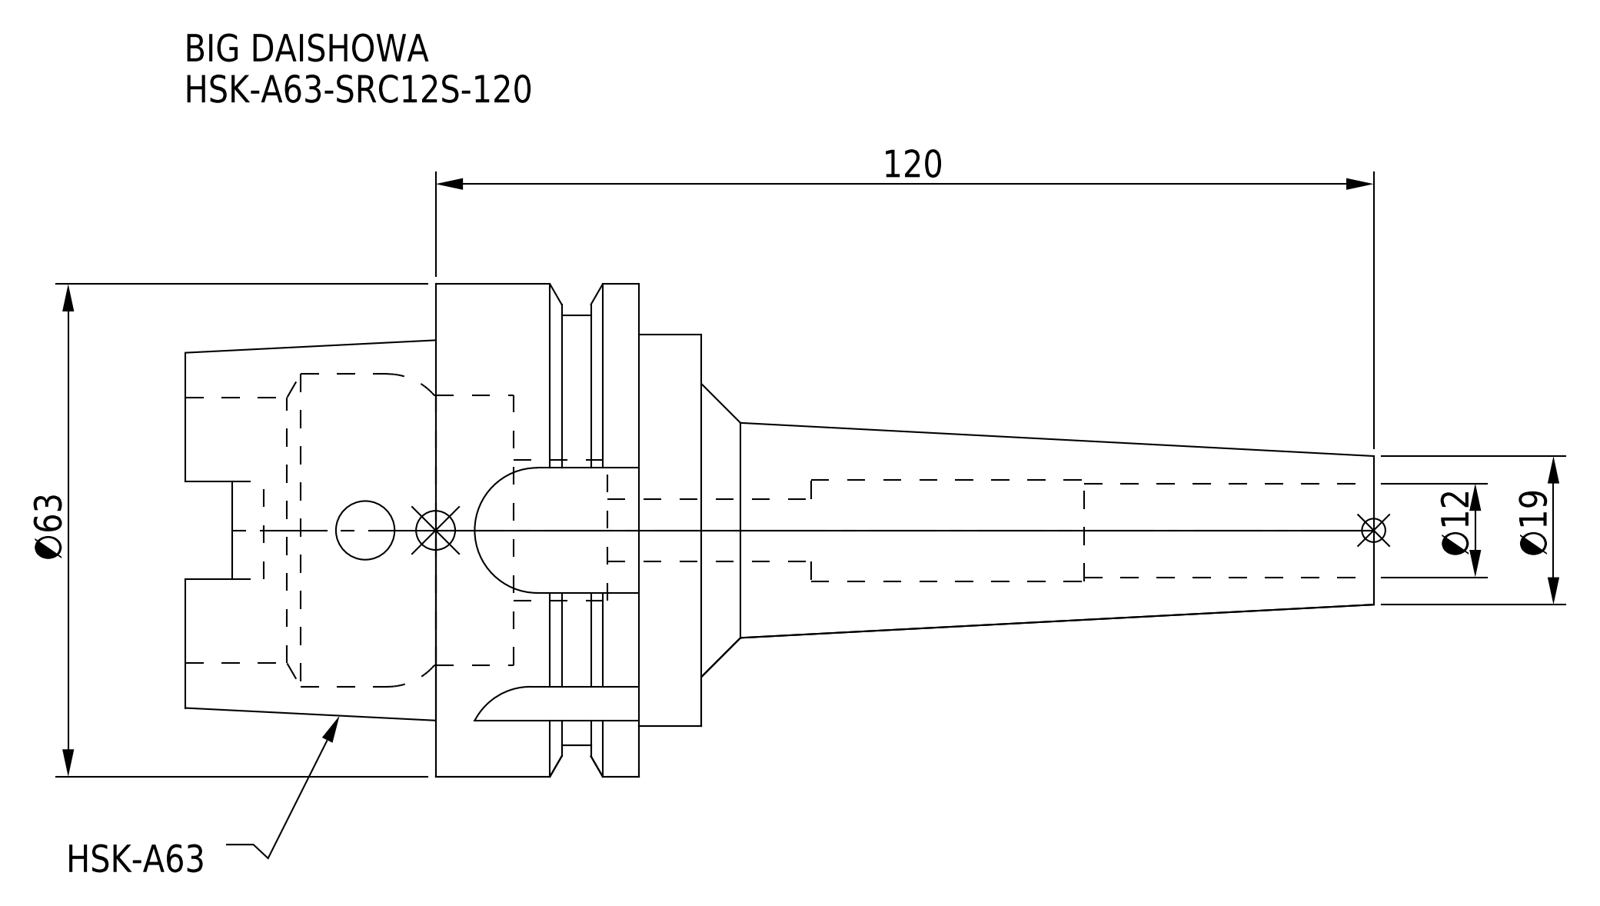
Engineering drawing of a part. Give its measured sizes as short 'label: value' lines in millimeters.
name: HSK-A63-SRC12S-120
written by: CREO PARAMETRIC BY PTC INC, 2016380 (AUTOMOTIVE_DESIGN)
unit: mm
bodies: 1 solid, 94 faces (39 planar, 37 cylindrical, 18 other)
size: 152 × 63 × 63
volume: 126 327 mm³; area: 32 815 mm²
holes: 1× ⌀7.5, 1× ⌀8, 1× ⌀12, 1× ⌀13, 1× ⌀18, 1× ⌀34, 1× ⌀34.5, 1× ⌀40
bosses: 1× ⌀63, 1× ⌀55, 1× ⌀50
rounds: 4× R2.88, 4× R8
face distances: 26, 8, 34, 24.05, 16.05, 9.95, 66, 58, 41.95, 32
